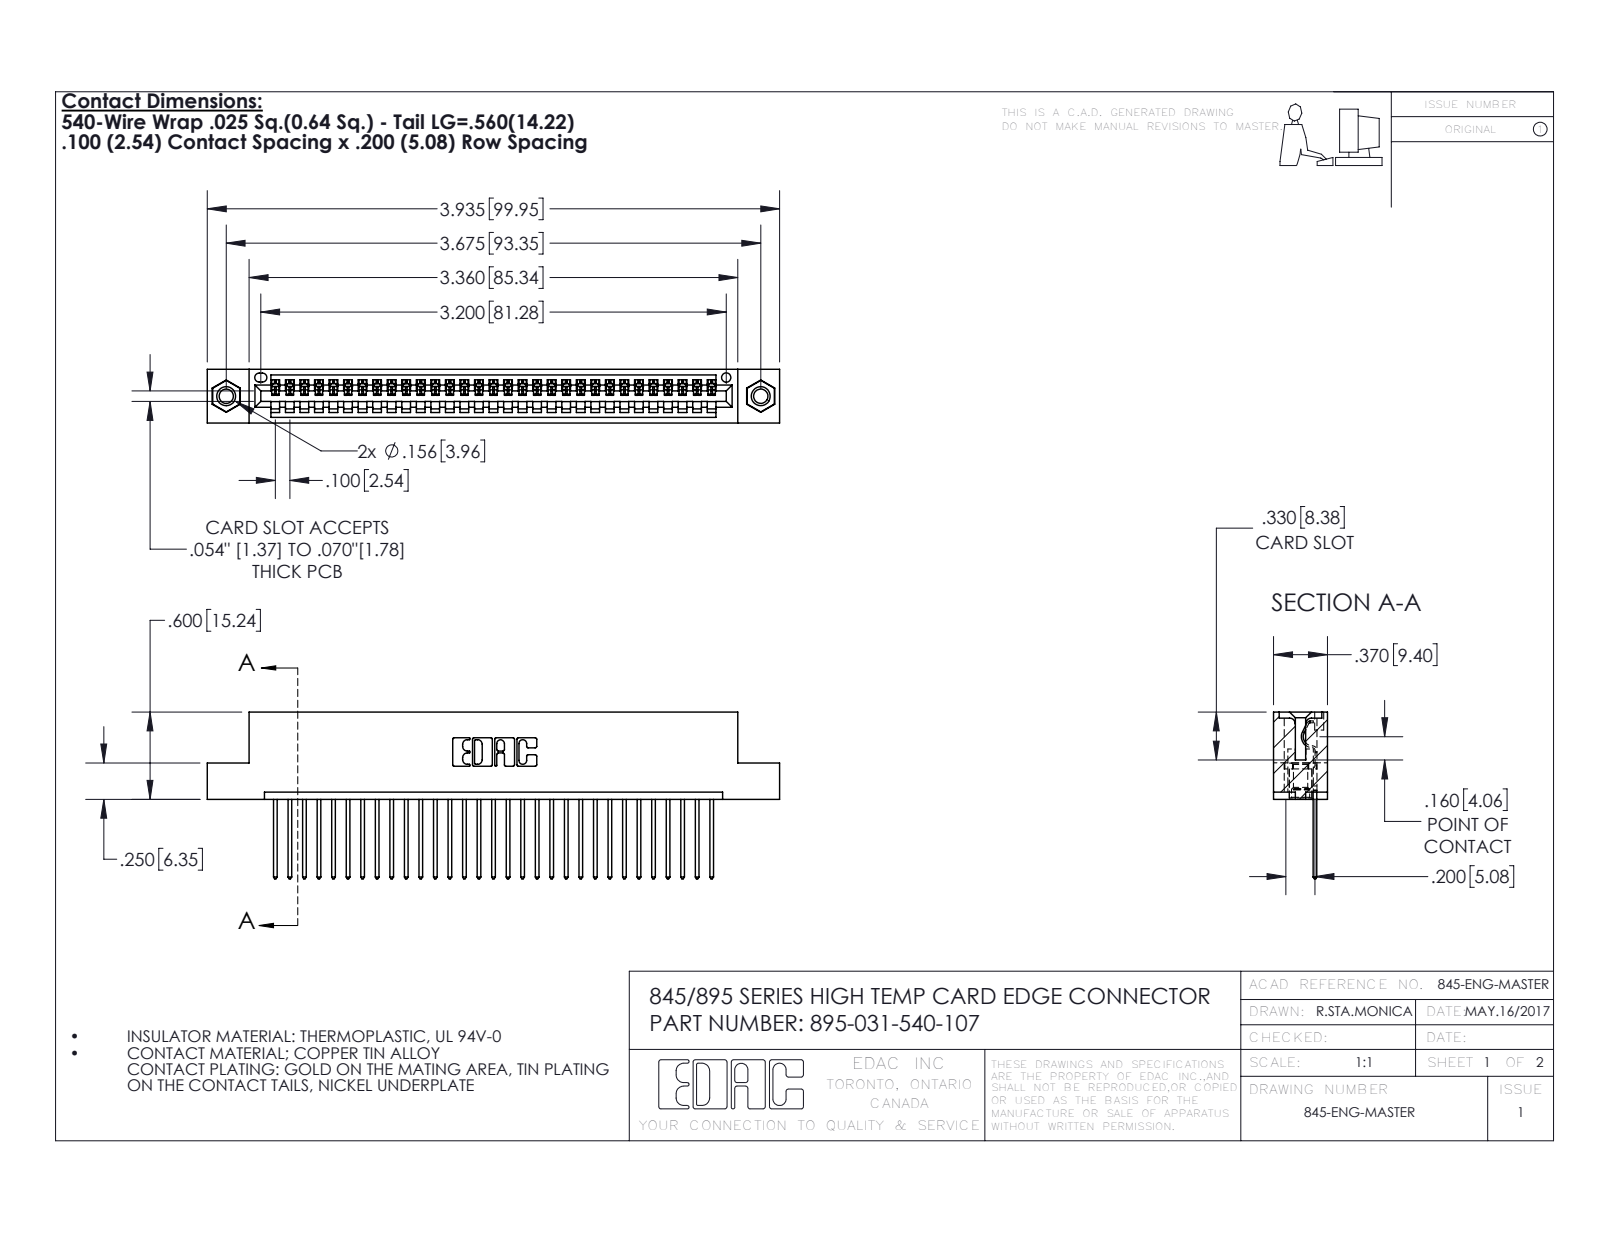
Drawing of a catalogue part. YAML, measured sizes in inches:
part_name: "345 Part_Flush Mounting Lugs - 0.156 Dia-TI; 345-292-001_345-293-140; 395-031-540-107; 345-250-001_345-250-005-103"
step_written_by: "SolidWorks 2016 (CONFIG_CONTROL_DESIGN)"
units: inches
bodies: {solids: 34, faces: 1984, planar: 1352, cylindrical: 616, other: 16}
overall_size: [3.935, 1.147, 0.37]
volume: 0.576
surface_area: 19.71
round_holes:
  - {diameter: 0.098, count: 2}
  - {diameter: 0.125, count: 2}
  - {diameter: 0.156, count: 2}
  - {diameter: 0.064, count: 1}
round_bosses_or_shafts:
  - {diameter: 0.155, count: 2}
partial_cylinders:
  - {radius: 0.006, count: 62}
  - {radius: 0.01, count: 62}
  - {radius: 0.01, count: 22}
  - {radius: 0.007, count: 6}
  - {radius: 0.031, count: 6}
  - {radius: 0.026, count: 3}
  - {radius: 0.031, count: 2}
  - {radius: 0.04, count: 2}
face_to_face_distances: [0.072, 0.298, 0.2, 0.37, 0.098, 0.272, 0.025, 0.225, 0.149, 0.072]
hole_center_spacings: [0.27, 3.44, 3.675]
